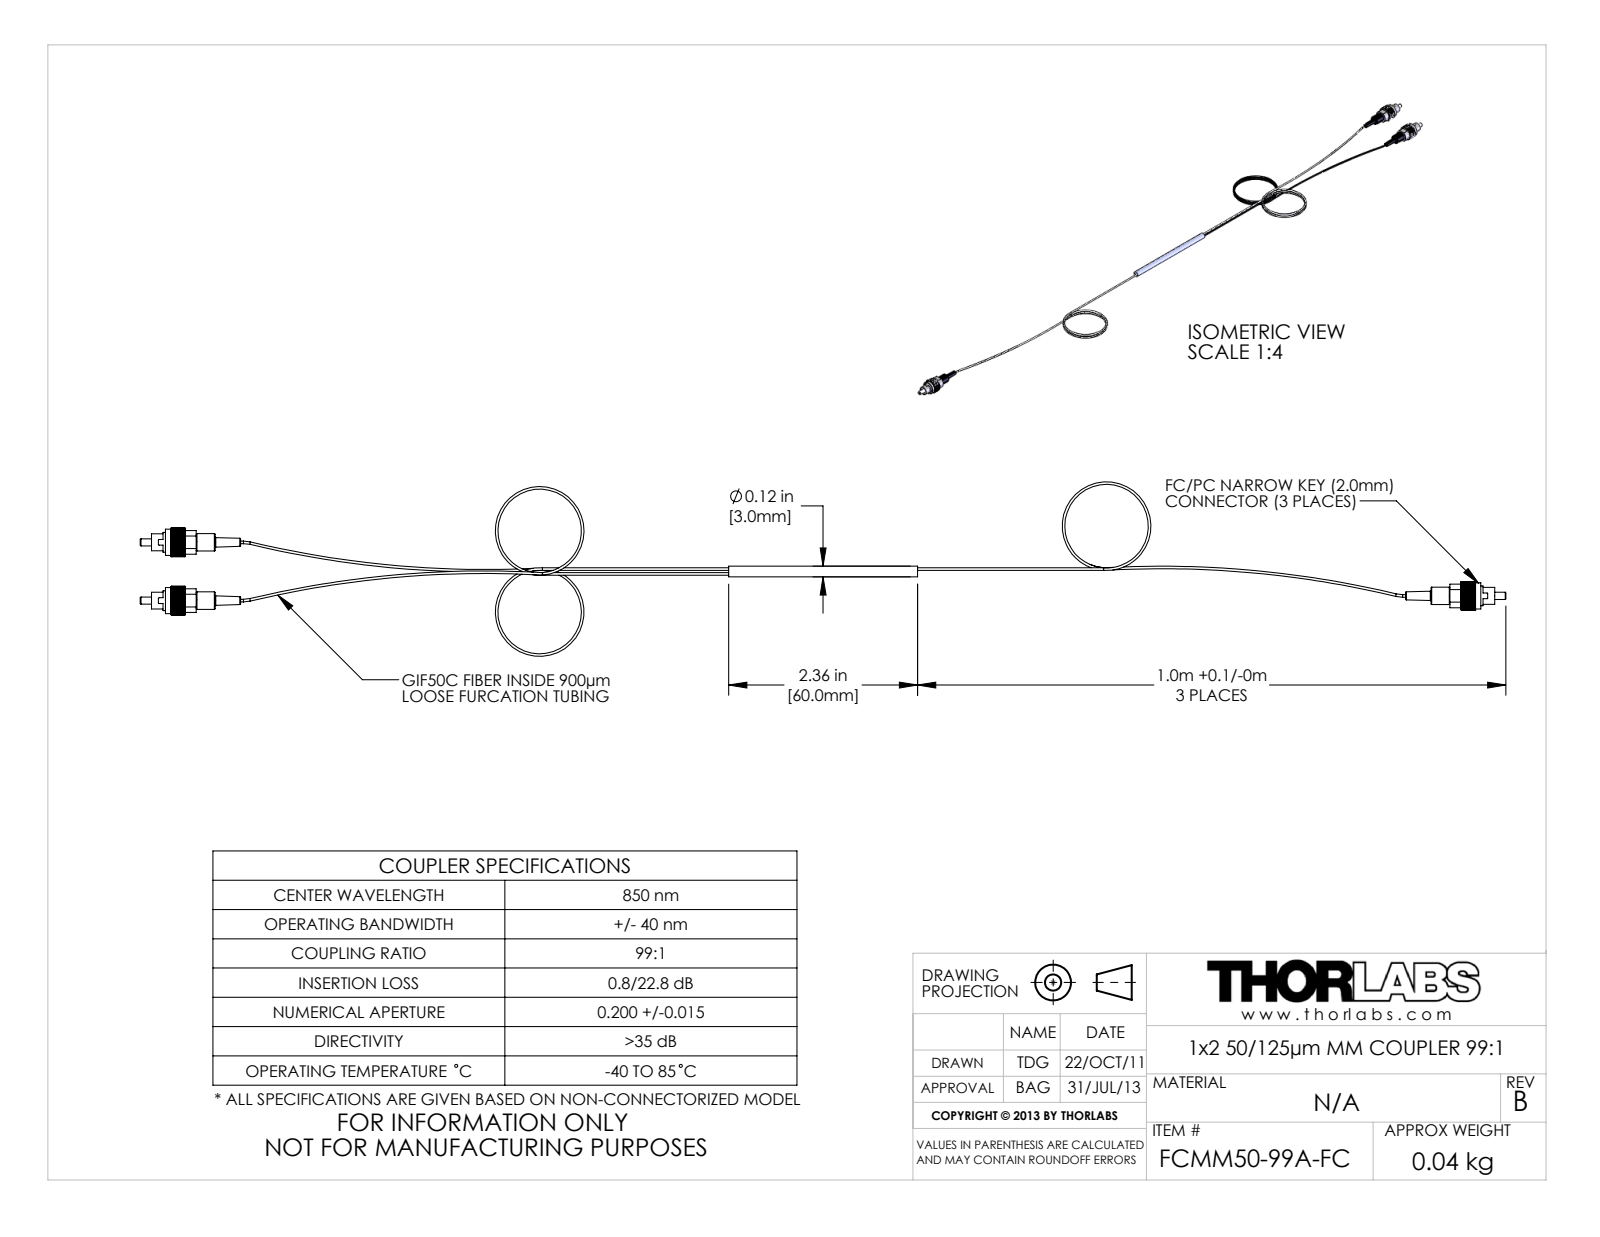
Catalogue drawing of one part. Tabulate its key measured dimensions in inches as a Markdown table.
| quantity | value |
| --- | --- |
| part name | 13900-E0W |
| STEP written by | SolidWorks 2012 (CONFIG_CONTROL_DESIGN) |
| units | inches |
| bodies | 13 solids, 904 faces (460 planar, 348 cylindrical, 96 other) |
| overall size | 18.778 × 2.4 × 0.63 |
| volume | 0.228 in³ |
| surface area | 16.9 in² |
| round holes (diameter × count) | 0.056 × 3, 0.192 × 3, 0.21 × 3, 0.25 × 3, 0.27 × 3, 0.325 × 3, 0.36 × 3, 0.039 × 2, 0.13 × 1 |
| round bosses / shafts (diameter × count) | 0.035 × 5, 0.272 × 3, 0.24 × 3, 0.232 × 3, 0.19 × 3, 0.157 × 3, 0.141 × 3, 0.098 × 3 |
| partial cylindrical surfaces (radius × count) | 0.01 × 6, 0.197 × 3, 0.163 × 2 |
| main face-to-face distances | 0.267, 0.267, 0.263, 0.116, 0.147, 0.031, 0.513, 0.397, 0.25, 17.648 |
| hole center spacings | 0.386, 0.033, 0.417, 0.449, 0.065, 0.245, 0.325, 0.355 |
